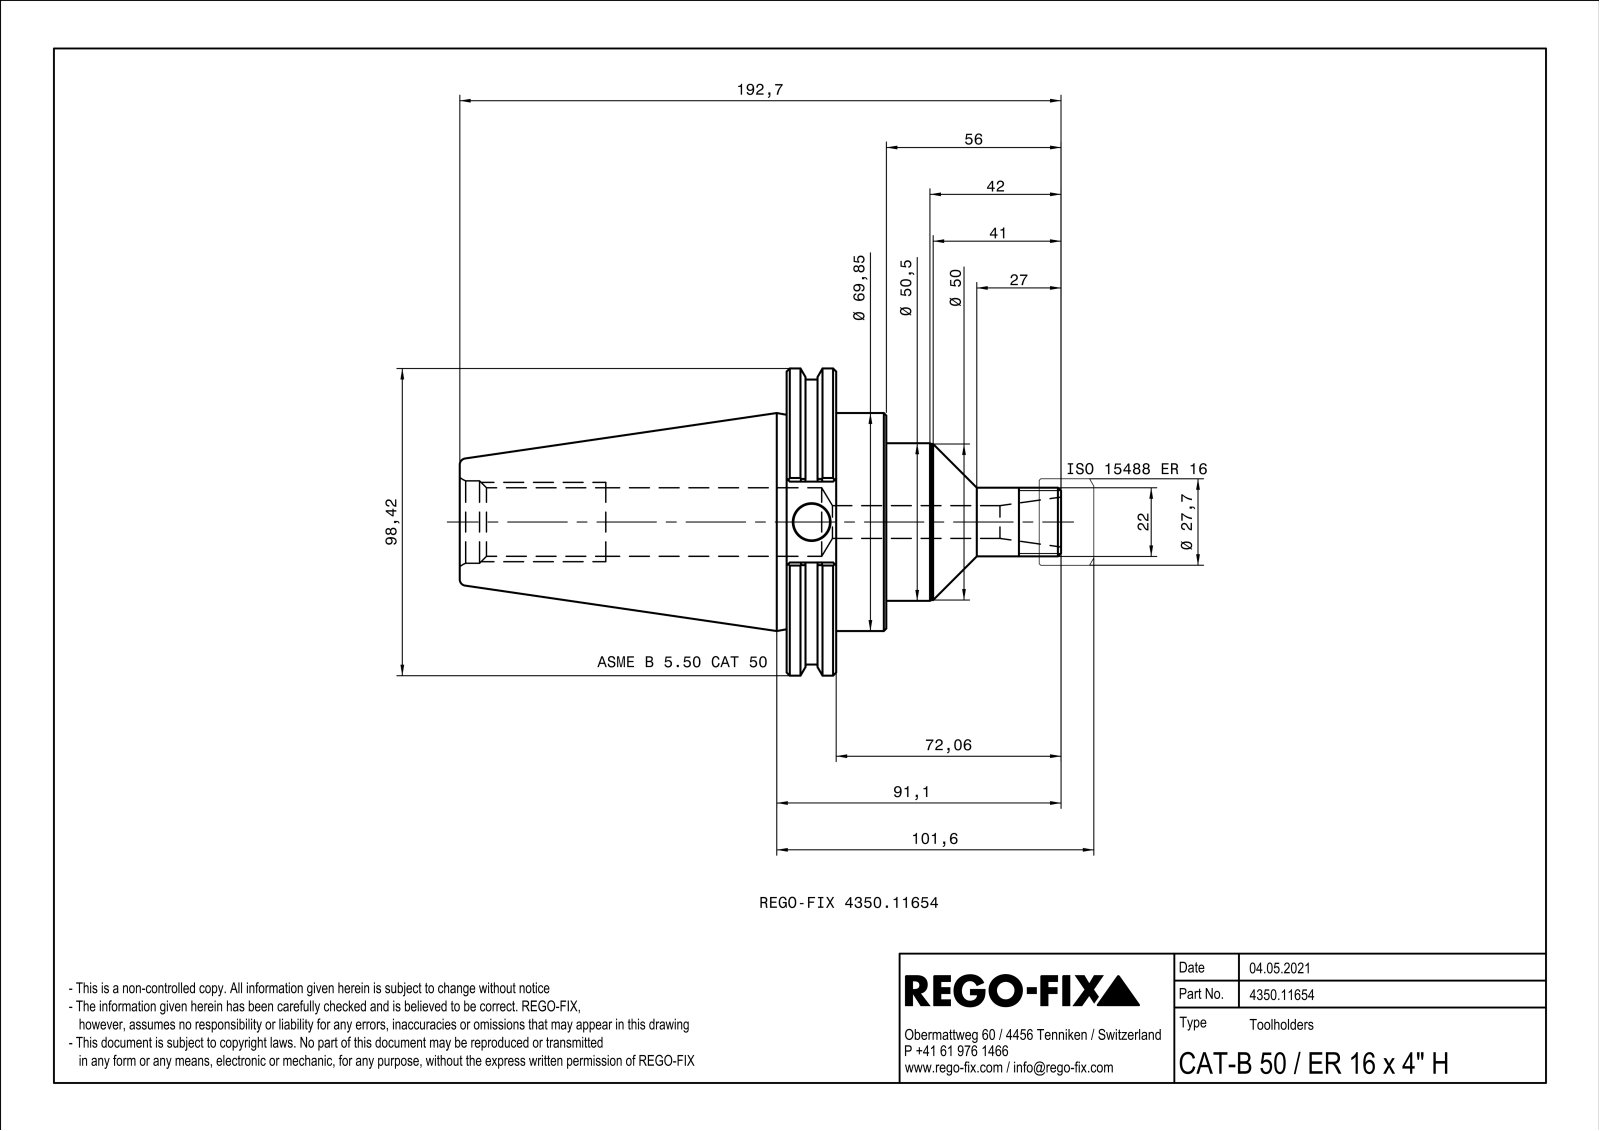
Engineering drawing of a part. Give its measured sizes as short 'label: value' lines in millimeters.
name: NOCUT
written by: SIEMENS PLM Software Solid Edge ST10 (AUTOMOTIVE_DESIGN)
unit: mm
bodies: 1 solid, 120 faces (36 planar, 42 cylindrical, 42 other)
size: 192.7 × 98.42 × 94.39
volume: 426 078 mm³; area: 55 914 mm²
holes: 2× ⌀3.24, 2× ⌀3.9, 1× ⌀10.5, 1× ⌀11.7, 1× ⌀21.96, 1× ⌀21.96, 1× ⌀26.4
bosses: 1× ⌀98.42, 1× ⌀91.3, 1× ⌀69.85, 1× ⌀50.5, 1× ⌀50, 1× ⌀22
rounds: 12× R0.5
face distances: 15.87, 16.06, 31.93, 136.7, 120.64, 104.77, 72.73, 25.92, 56, 72.06
